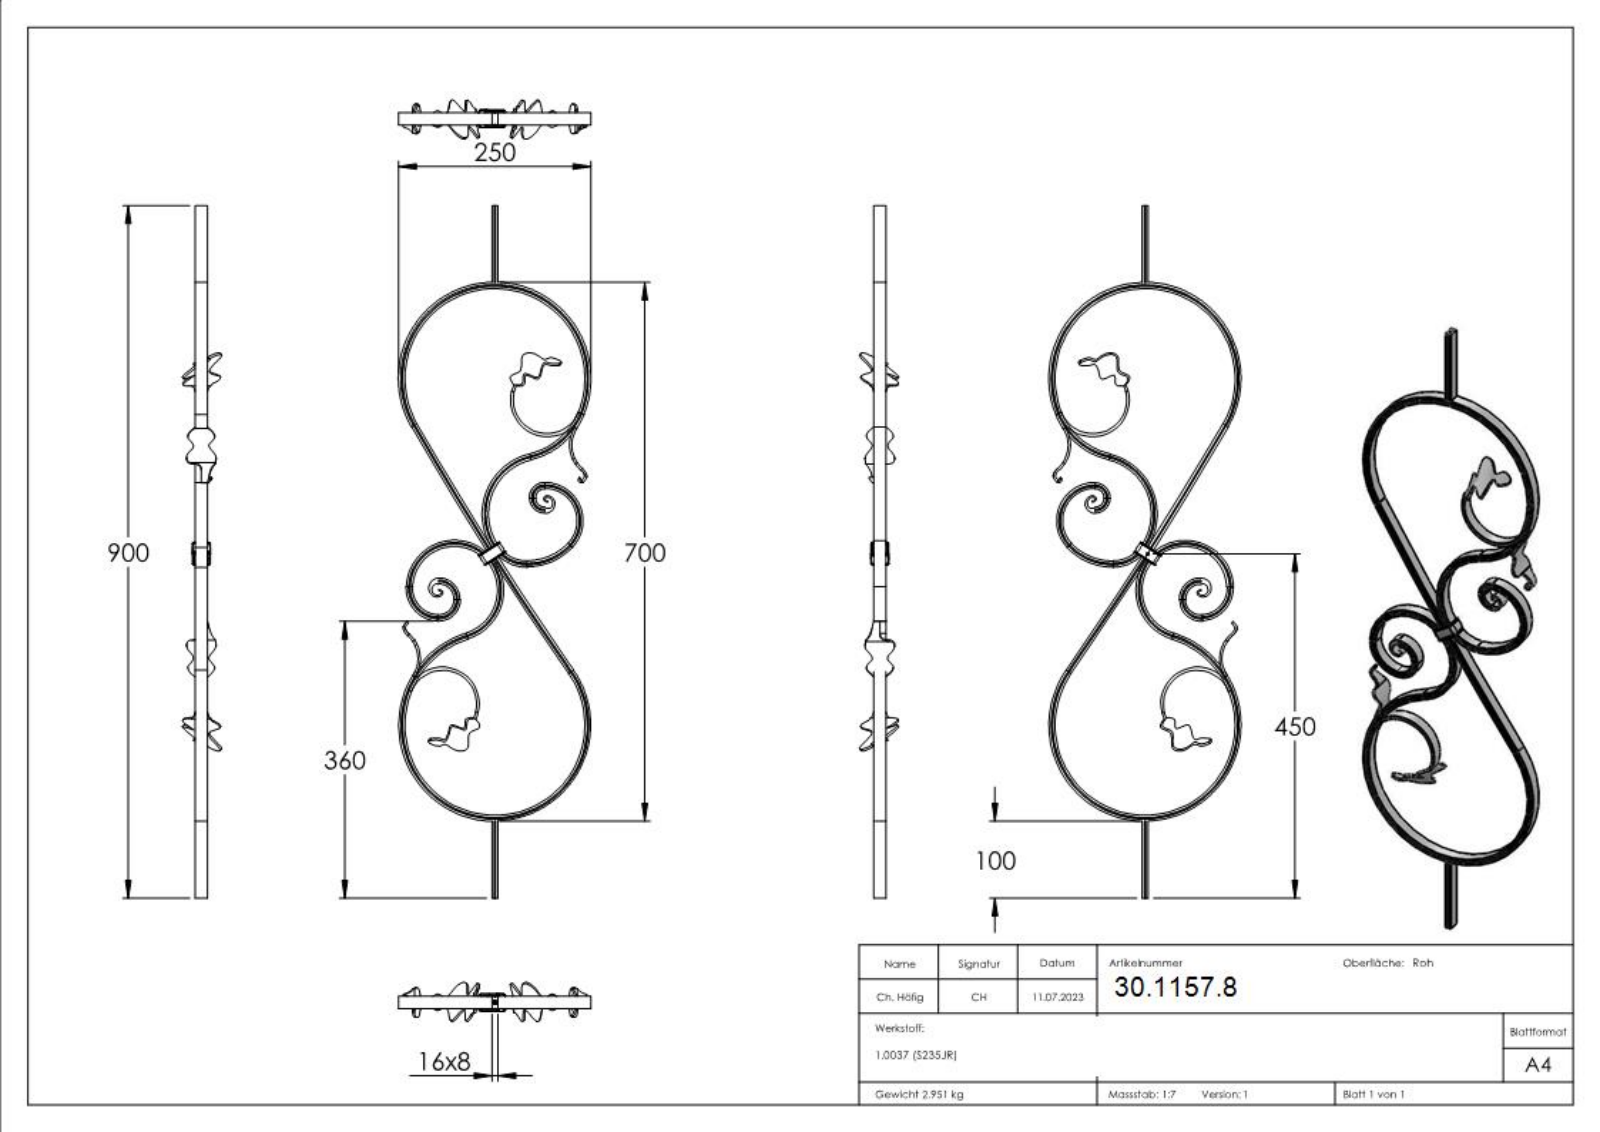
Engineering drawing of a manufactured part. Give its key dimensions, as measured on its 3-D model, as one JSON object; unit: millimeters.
{"part_name": "1601", "step_written_by": "SolidWorks 2018 (CONFIG_CONTROL_DESIGN)", "units": "millimeters", "bodies": {"solids": 8, "faces": 611, "planar": 267, "cylindrical": 98, "other": 246}, "overall_size": [900, 250, 51.33], "volume_mm3": 400361, "surface_area_mm2": 182132, "round_holes": [[234, 1]], "partial_cylinders_radius": [[0.5, 28], [0.2, 8], [1, 5], [4, 4], [21.62, 4], [10, 3], [20, 2], [125, 2]], "face_to_face_distances": [16, 8, 0.5, 16.5, 9.9, 8.5, 17, 26.5, 900, 16.01]}
